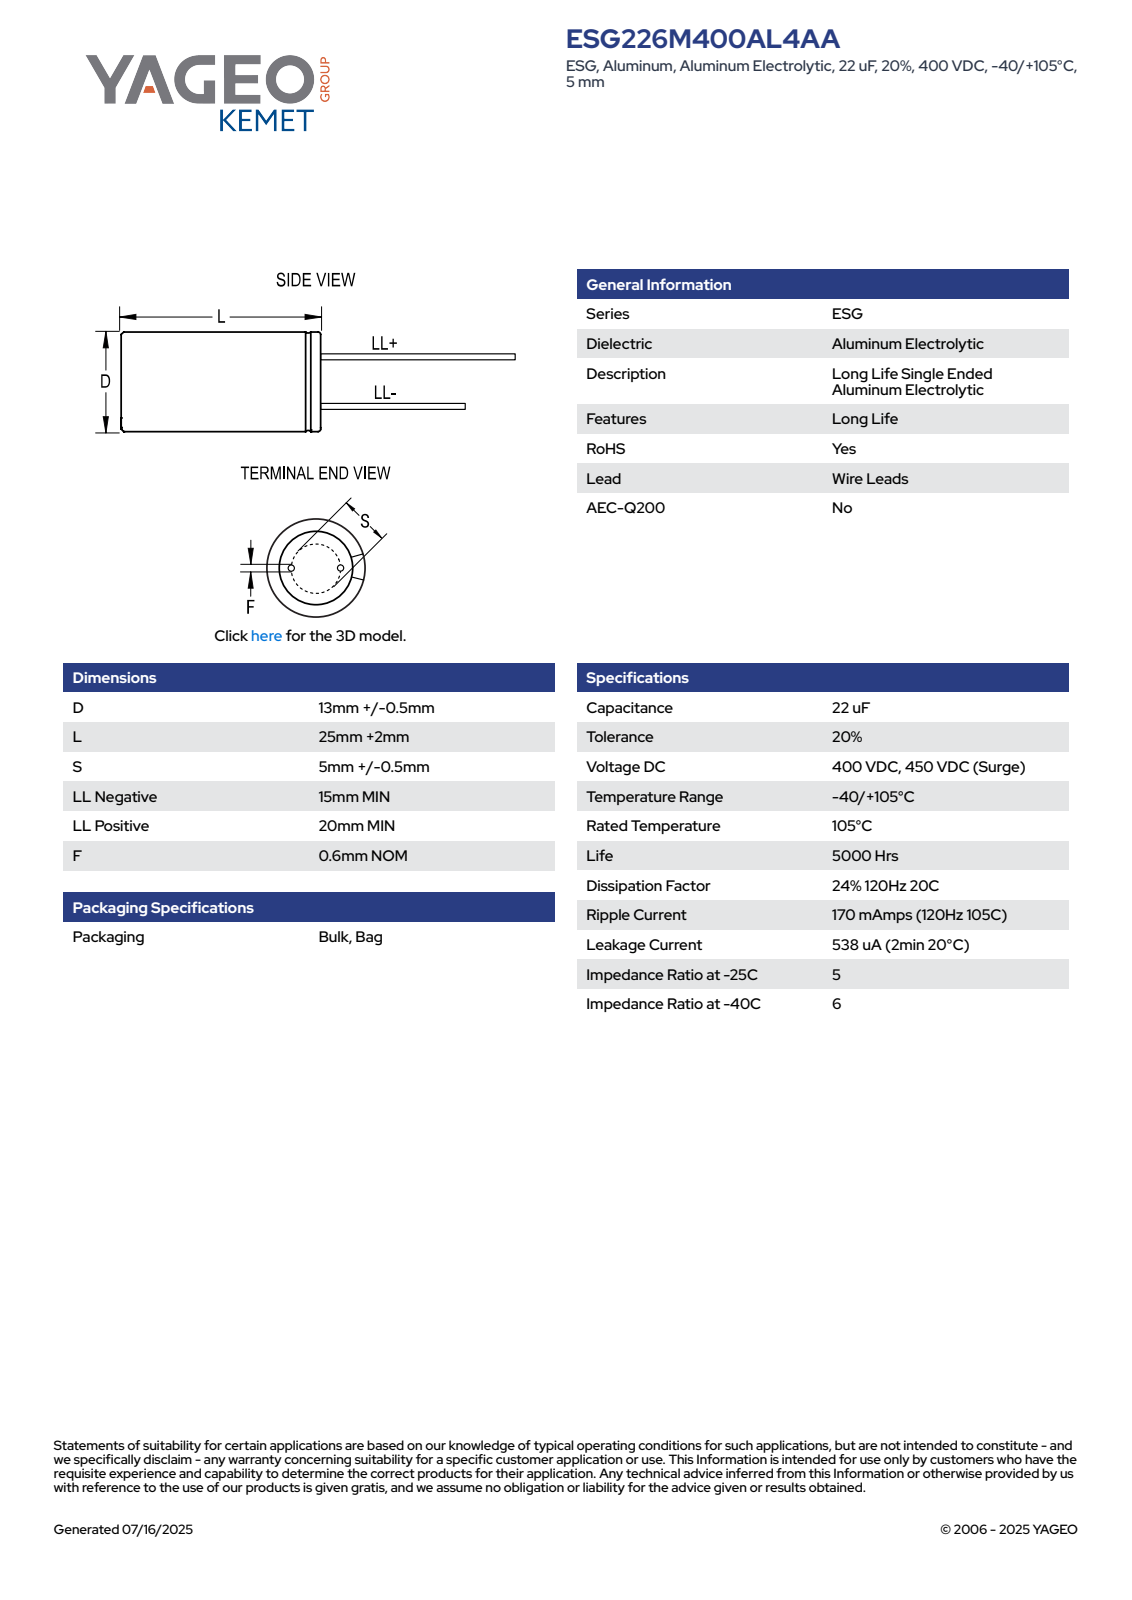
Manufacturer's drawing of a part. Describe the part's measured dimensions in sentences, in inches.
The part is named "CAR_KLP_13X25_D13.5L27S5F0.6". Its 3-D file was written by "SolidWorks 2014 (AUTOMOTIVE_DESIGN)". It is 4 solids with 75 faces: 61 planar, 8 cylindrical and 6 other. Overall it measures 1.851 by 0.531 by 0.531 inches. Its volume is 0.235 cubic inches and its surface area 2.385 square inches. Round bosses or shafts: 2 of diameter 0.024, 1 of diameter 0.531. The main face-to-face distances are 1.063, 1.063, 1.654, 1.851, 1.654, 1.85, 0.591, 0.787, 0.197, 0.071.
